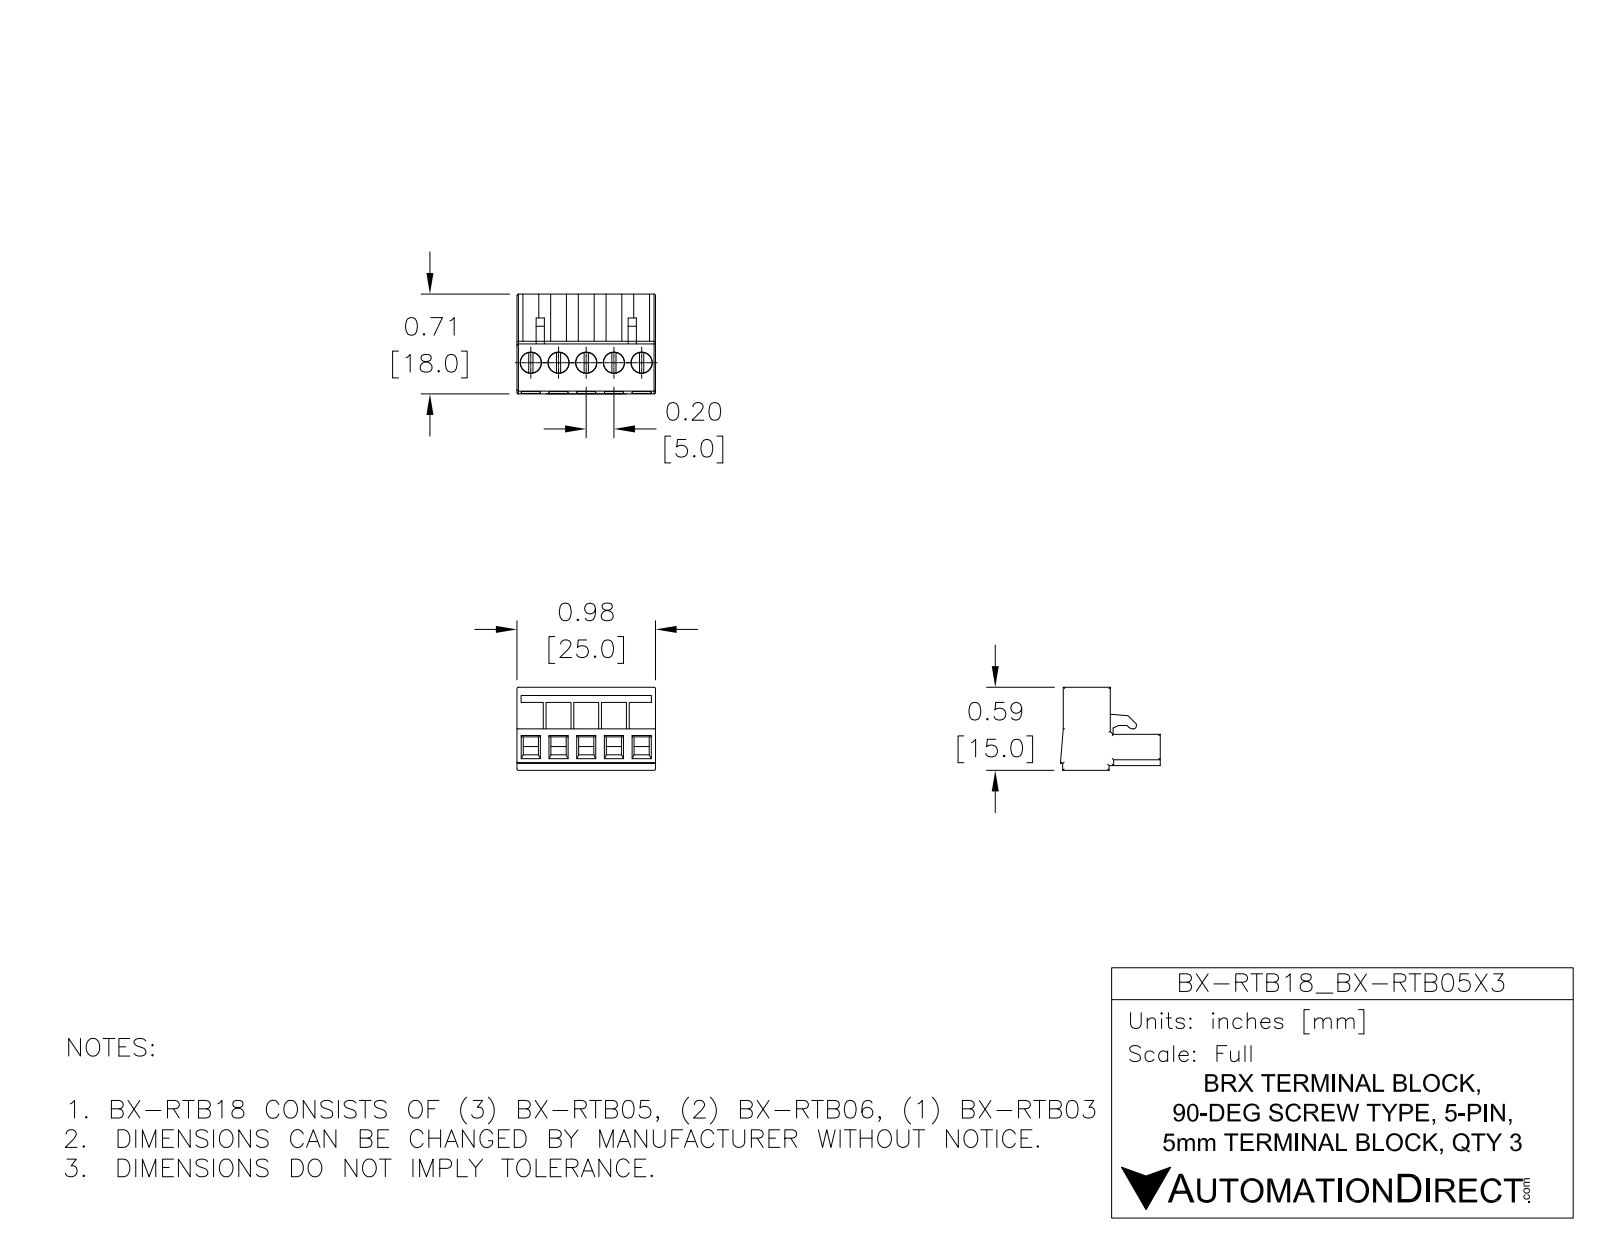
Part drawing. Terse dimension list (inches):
name: BX-RTB18
written by: SolidWorks 2017 (AUTOMOTIVE_DESIGN)
unit: in
bodies: 6 solids, 1740 faces (1188 planar, 492 cylindrical, 60 other)
size: 8.406 × 0.709 × 0.591
volume: 1.399 in³; area: 28.4 in²
holes: 30× ⌀0.063, 30× ⌀0.124, 30× ⌀0.152
bosses: 30× ⌀0.148
rounds: 169× R0.01, 30× R0.099, 1× R0.02, 1× R0.039
face distances: 0.335, 0.591, 1.484, 0.224, 0.366, 0.5, 0.256, 2.969, 0.354, 0.031
hole spacings: 0.197, 1.484, 1.681, 1.287, 0.394, 2.969, 1.878, 3.165
